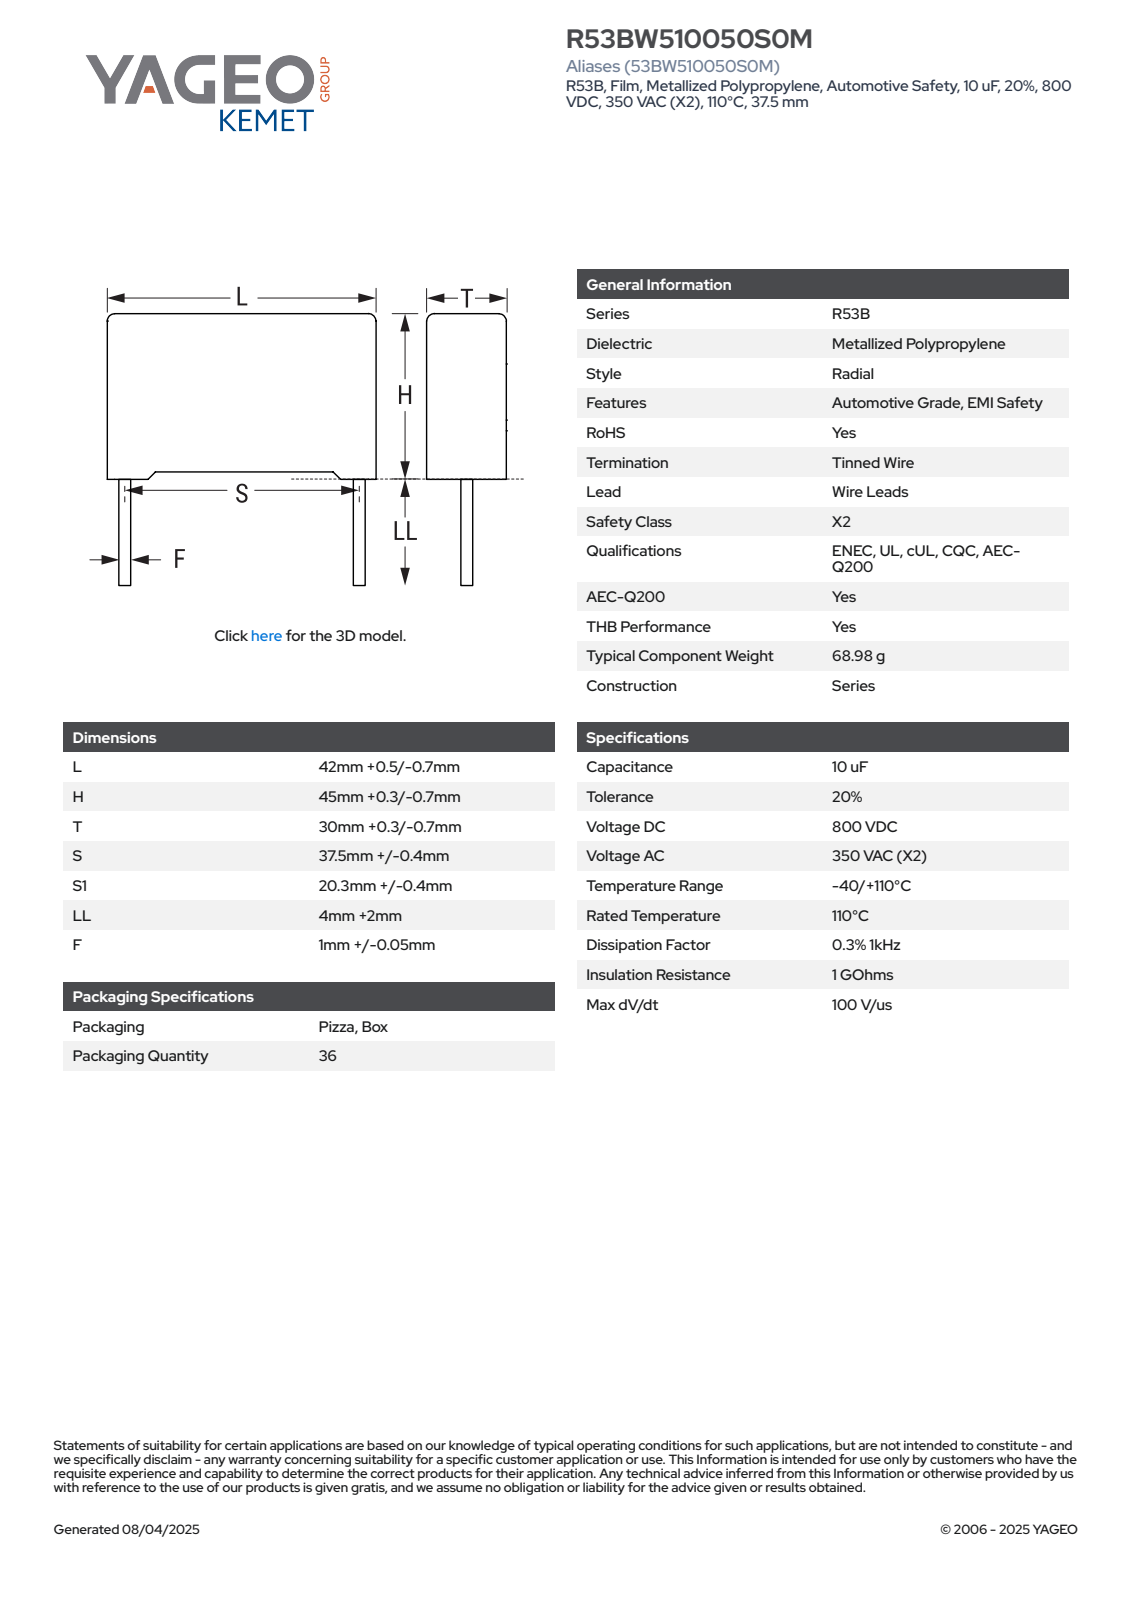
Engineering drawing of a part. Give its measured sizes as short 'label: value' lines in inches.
name: CFR_RB2_42X45X30_L42.5H45.3T30.3S37.5LL6F1.05
written by: SolidWorks 2021 (AUTOMOTIVE_DESIGN)
unit: in
bodies: 4 solids, 85 faces (77 planar, 8 cylindrical, 0 other)
size: 2.02 × 1.673 × 1.193
volume: 3.457 in³; area: 14.4 in²
bosses: 2× ⌀0.041
rounds: 4× R0.02
face distances: 1.193, 1.673, 1.722, 0.032, 1.754, 0.03, 0.061, 1.783, 0.056, 1.617
